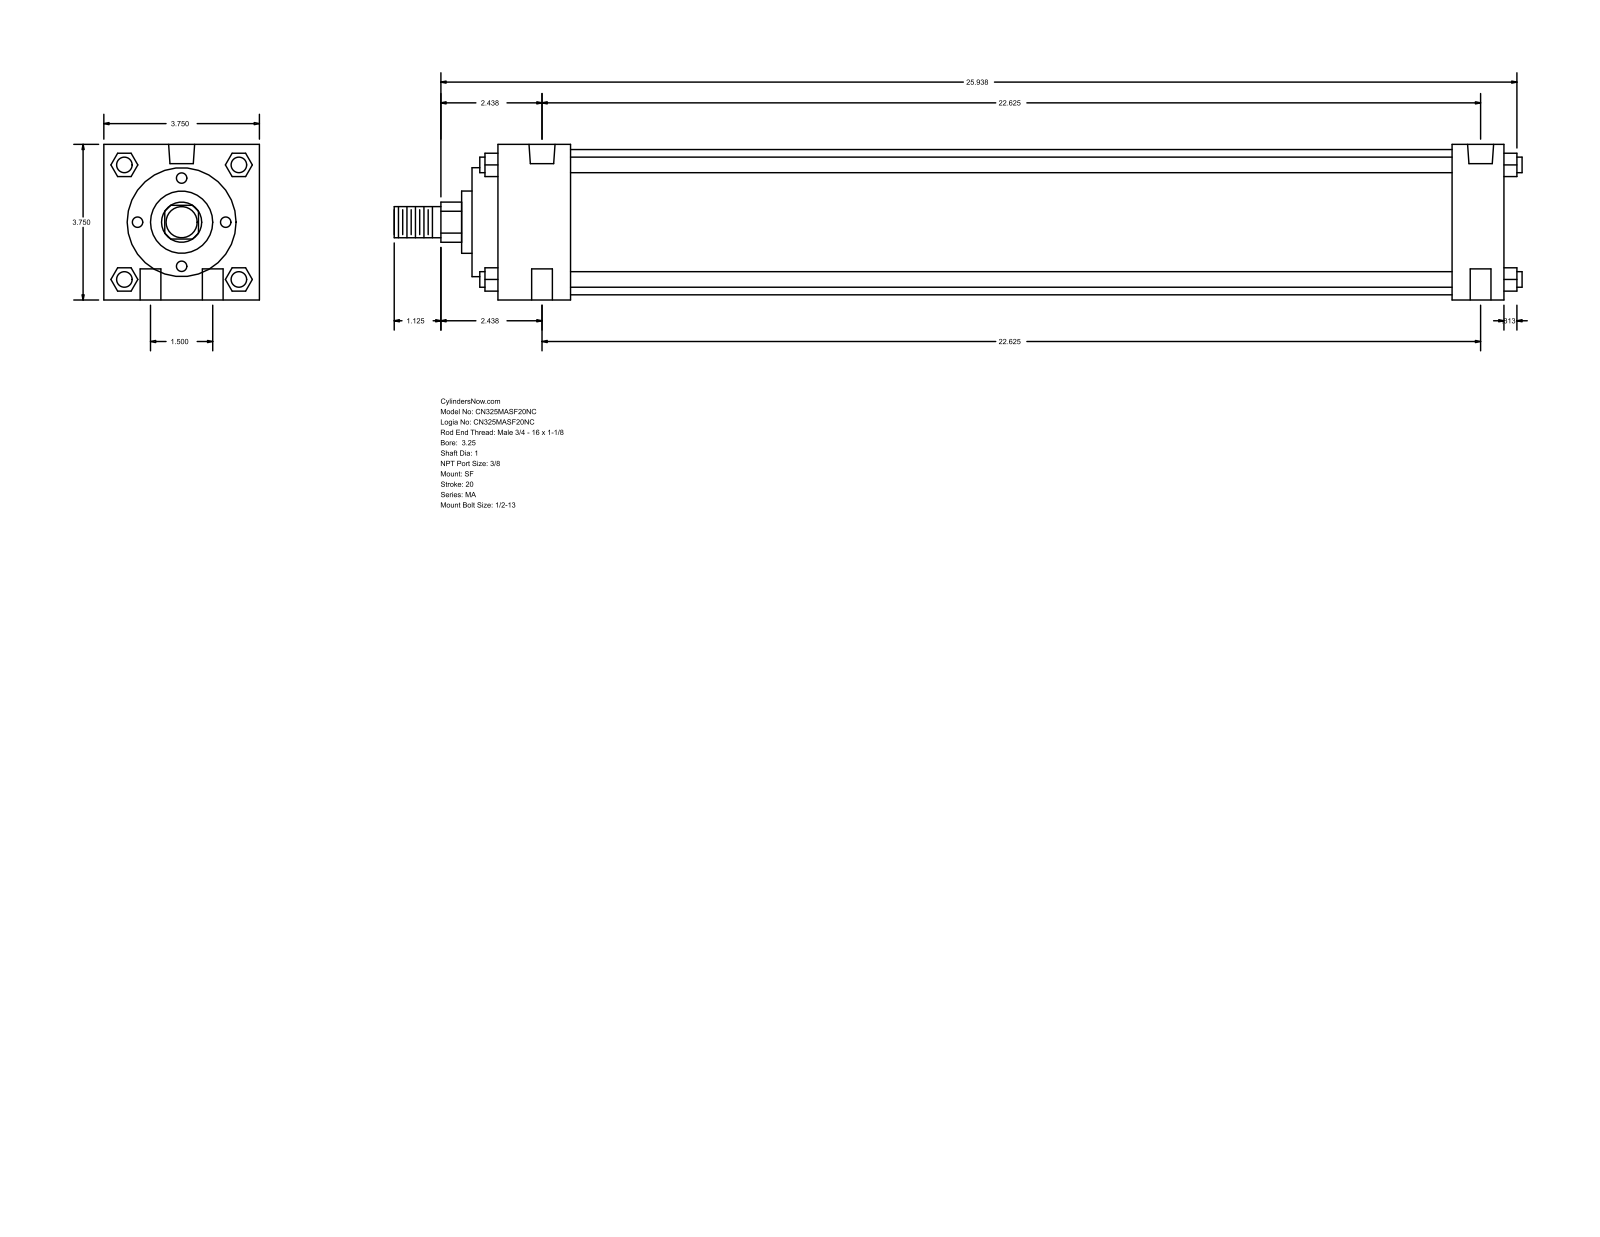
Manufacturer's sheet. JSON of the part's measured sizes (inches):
{"part_name": "MA_SF__0325_1", "step_written_by": "GSSL Pune (CONFIG_CONTROL_DESIGN)", "units": "inches", "bodies": {"solids": 0, "faces": 126, "planar": 95, "cylindrical": 31, "other": 0}, "overall_size": [27.187, 3.75, 3.75], "round_holes": [[0.5, 4], [0.437, 2], [0.627, 2]], "round_bosses_or_shafts": [[0.375, 4], [3.5, 1], [2.625, 1], [1.5, 1], [1, 1], [0.75, 1]], "partial_cylinders_radius": [[0.484, 1]], "face_to_face_distances": [3.75, 24.25, 23, 1.25, 1.75, 21.25, 22.5, 0.625, 2.375, 23.625], "hole_center_spacings": [0.75, 22.638, 22.625, 1.5, 22.675, 22.25]}
